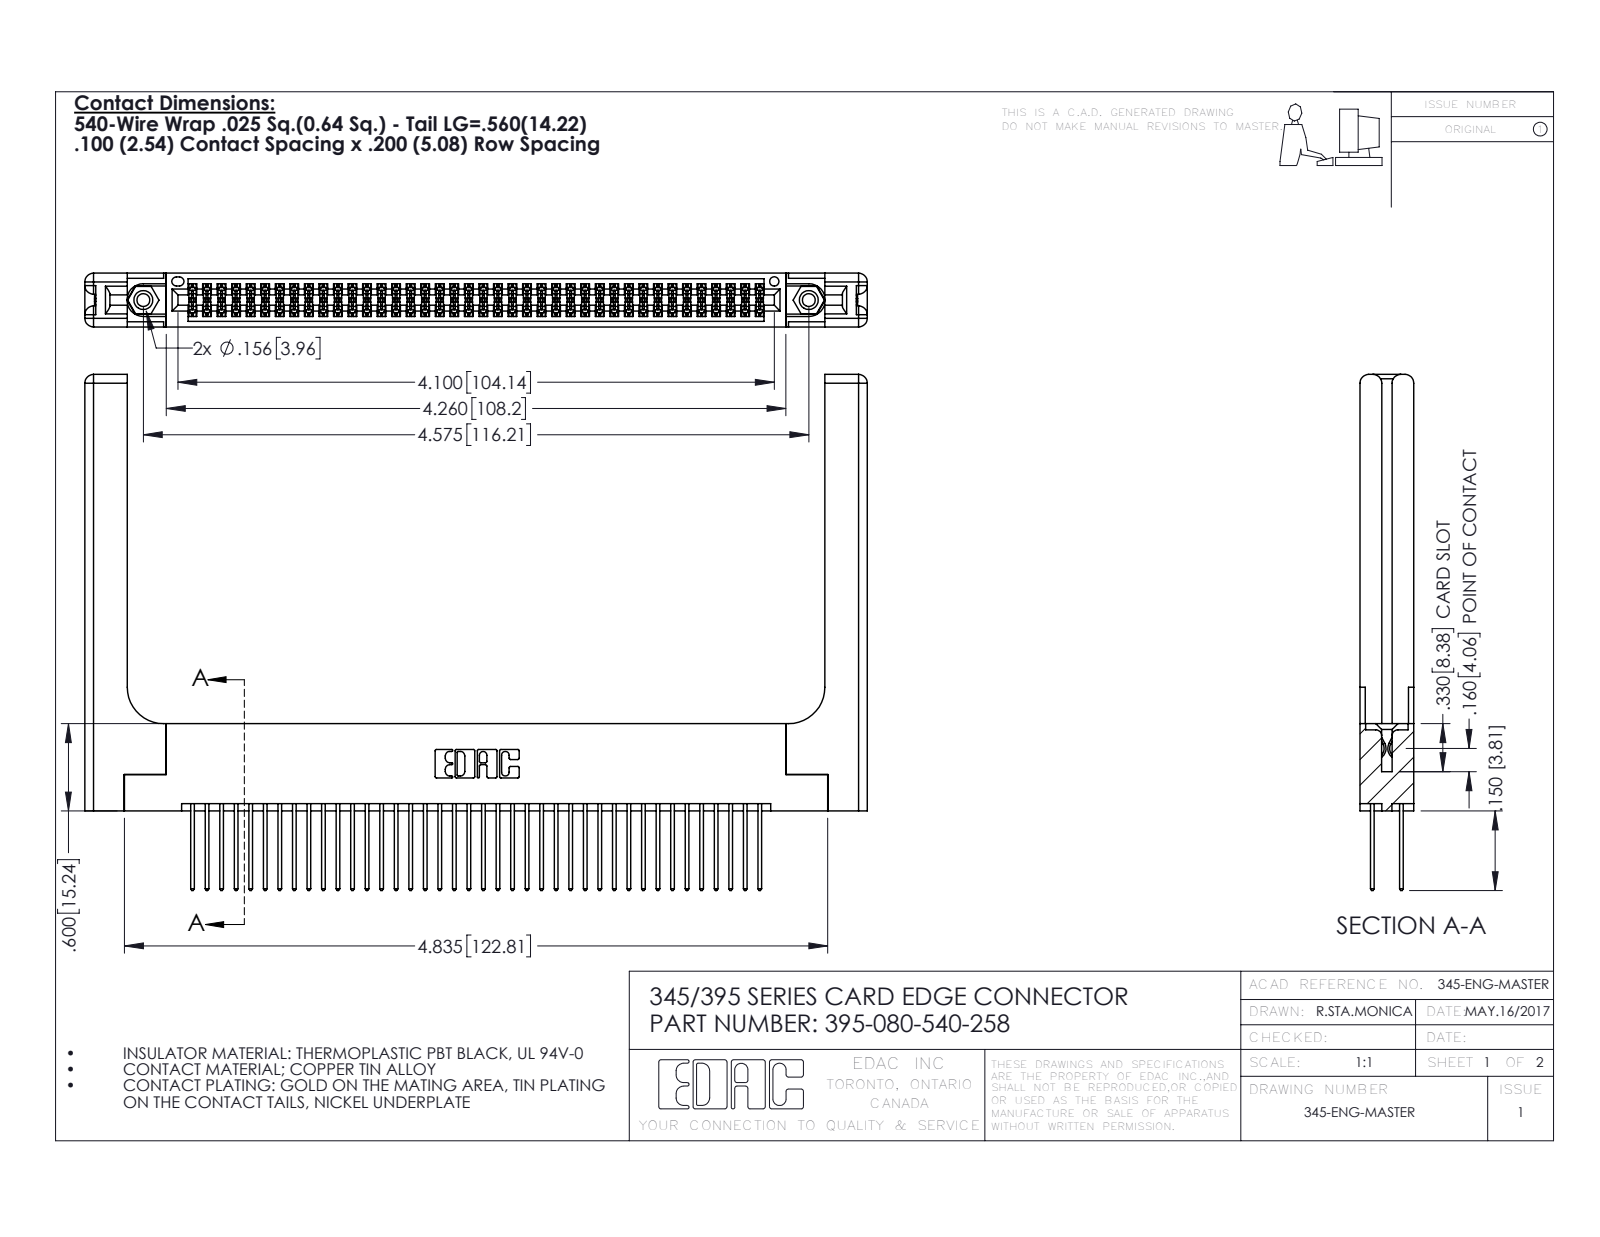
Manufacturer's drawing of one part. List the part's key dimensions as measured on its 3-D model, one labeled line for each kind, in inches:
Part name (STEP PRODUCT): 345 Part_Flush Mounting Lugs - 0.156 Dia-TH; 345-250-001_345-250-001-102; 395-080-540-258; 345-220-058_345-220-058 (+1 more)
STEP written by: SolidWorks 2016 (CONFIG_CONTROL_DESIGN)
Units: inches
Bodies: 85 solids, 4382 faces (2868 planar, 1454 cylindrical, 60 other)
Overall size (bounding box): 5.379 × 3.547 × 0.37
Volume: 1.344 in³ · Surface area: 41.02 in²
Round holes (diameter × count): ⌀0.089 ×2, ⌀0.125 ×2, ⌀0.156 ×2, ⌀0.064 ×1
Round bosses / shafts (diameter × count): ⌀0.155 ×2
Partial cylindrical surfaces — rounded edges, fillets, slot ends (radius × count): R0.006 ×120, R0.01 ×80, R0.01 ×22, R0.06 ×16, R0.007 ×6, R0.031 ×6, R0.026 ×3, R0.014 ×2
Main face-to-face distances: 0.072, 0.298, 0.37, 0.2, 0.098, 0.272, 0.025, 0.225, 0.175, 0.148
Hole centre spacings: 0.27, 4.339, 4.575
